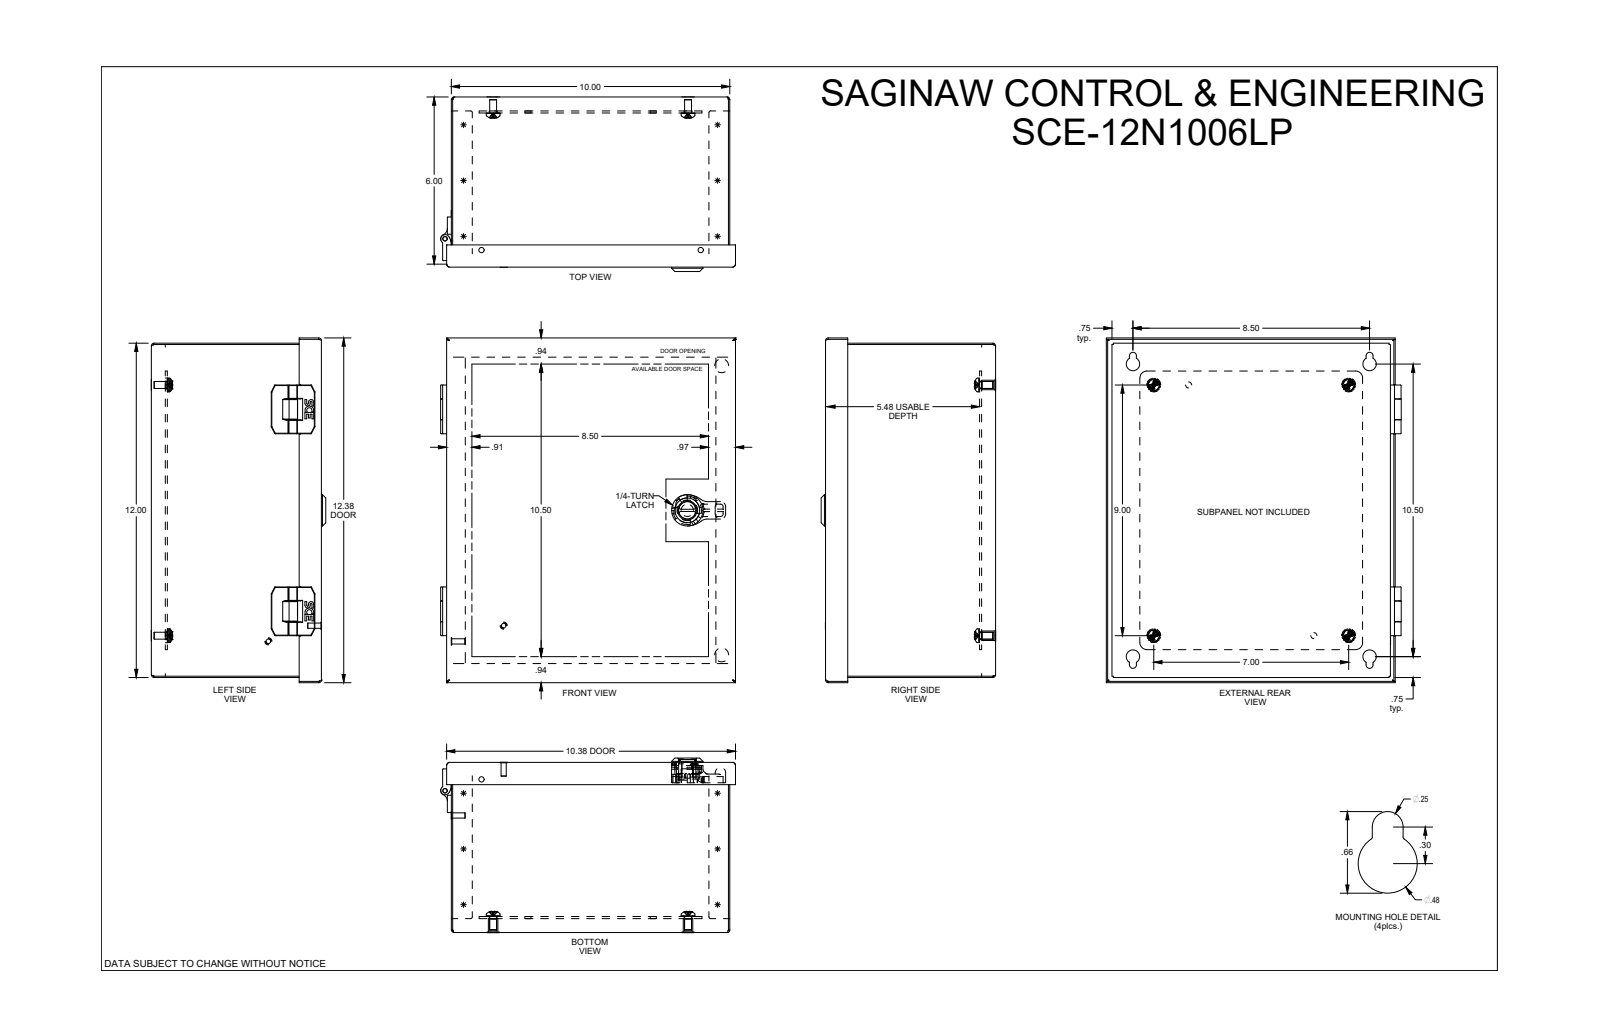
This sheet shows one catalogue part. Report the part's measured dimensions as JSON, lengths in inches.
{"part_name": "SCE-12N1006LP", "step_written_by": "SolidWorks 2019 (AUTOMOTIVE_DESIGN)", "units": "inches", "bodies": {"solids": 31, "faces": 1545, "planar": 578, "cylindrical": 643, "other": 324}, "overall_size": [12.375, 10.593, 6.267], "volume_in3": 41.4, "surface_area_in2": 1328, "round_holes": [[0.17, 4], [0.25, 4], [0.281, 4], [0.329, 4], [0.343, 4], [0.48, 4], [0.193, 3], [0.187, 2], [0.218, 2], [0.158, 1], [0.44, 1], [0.635, 1]], "round_bosses_or_shafts": [[0.492, 4], [0.479, 4], [0.341, 4], [0.248, 4], [0.237, 4], [0.16, 4], [0.5, 2], [0.323, 2]], "partial_cylinders_radius": [[0.01, 253], [0.02, 95], [0.06, 25], [0.015, 24], [0.025, 24], [0.055, 6], [0.25, 6], [0.125, 4]], "face_to_face_distances": [0.06, 6.047, 9.94, 11.94, 5.987, 6.107, 0.5, 0.44, 0.575, 0.515], "hole_center_spacings": [1.061, 7.786, 9.779, 12.455, 1.089, 1.091, 7.25, 7.331]}
